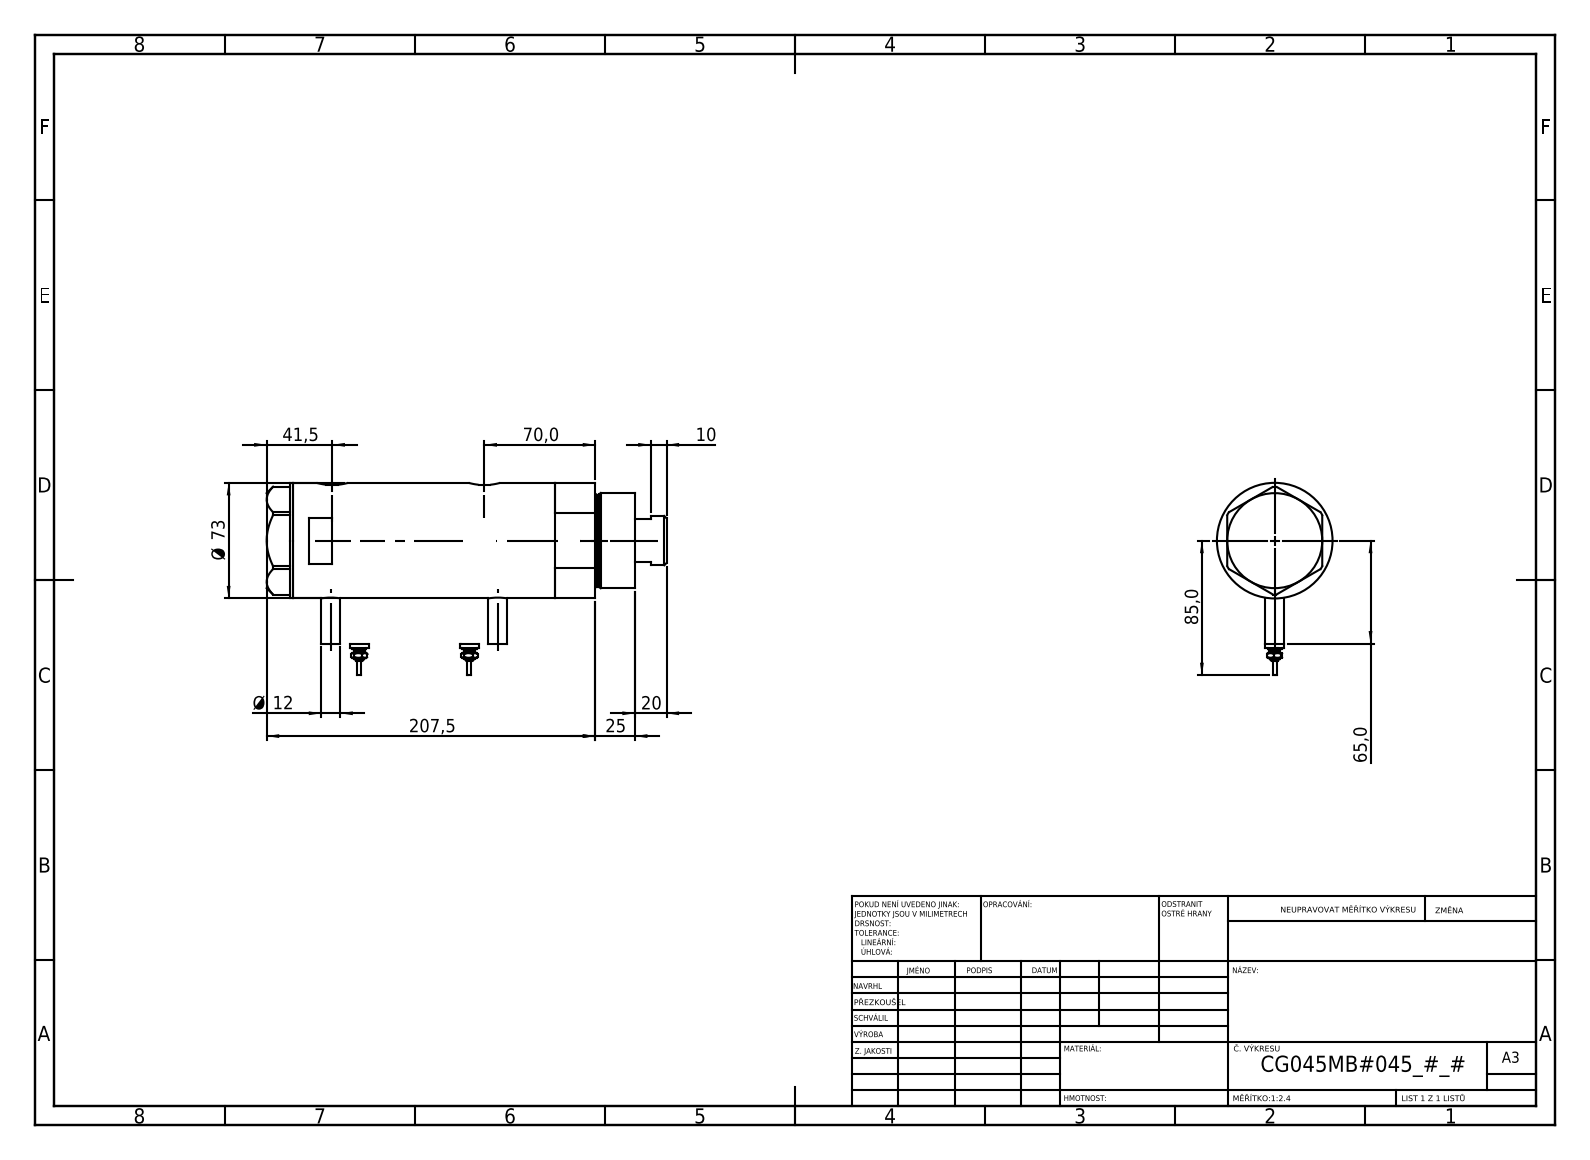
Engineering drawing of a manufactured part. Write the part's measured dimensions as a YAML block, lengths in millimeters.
part_name: "V270CG_MIDDLE; V270CG_FRONT; V270CG_VC; V270CG_BACK (+1 more)"
step_written_by: "SolidWorks 2019 (CONFIG_CONTROL_DESIGN)"
units: millimeters
bodies: {solids: 6, faces: 212, planar: 77, cylindrical: 71, other: 64}
overall_size: [252.5, 121.5, 73]
volume: 896090
surface_area: 151933
round_holes:
  - {diameter: 12.5, count: 2}
  - {diameter: 13.16, count: 2}
  - {diameter: 10.5, count: 1}
  - {diameter: 32, count: 1}
  - {diameter: 33.5, count: 1}
  - {diameter: 45, count: 1}
  - {diameter: 48, count: 1}
  - {diameter: 64, count: 1}
round_bosses_or_shafts:
  - {diameter: 12, count: 4}
  - {diameter: 9, count: 2}
  - {diameter: 7, count: 2}
  - {diameter: 4.5, count: 2}
  - {diameter: 2.5, count: 2}
  - {diameter: 73, count: 1}
  - {diameter: 60, count: 1}
  - {diameter: 58, count: 1}
partial_cylinders:
  - {radius: 10, count: 2}
face_to_face_distances: [95, 121, 26, 16.5, 42.5, 137.5, 2, 216, 232.5, 190]
hole_center_spacings: [1, 8.5, 96, 97, 104.5, 105.5]
